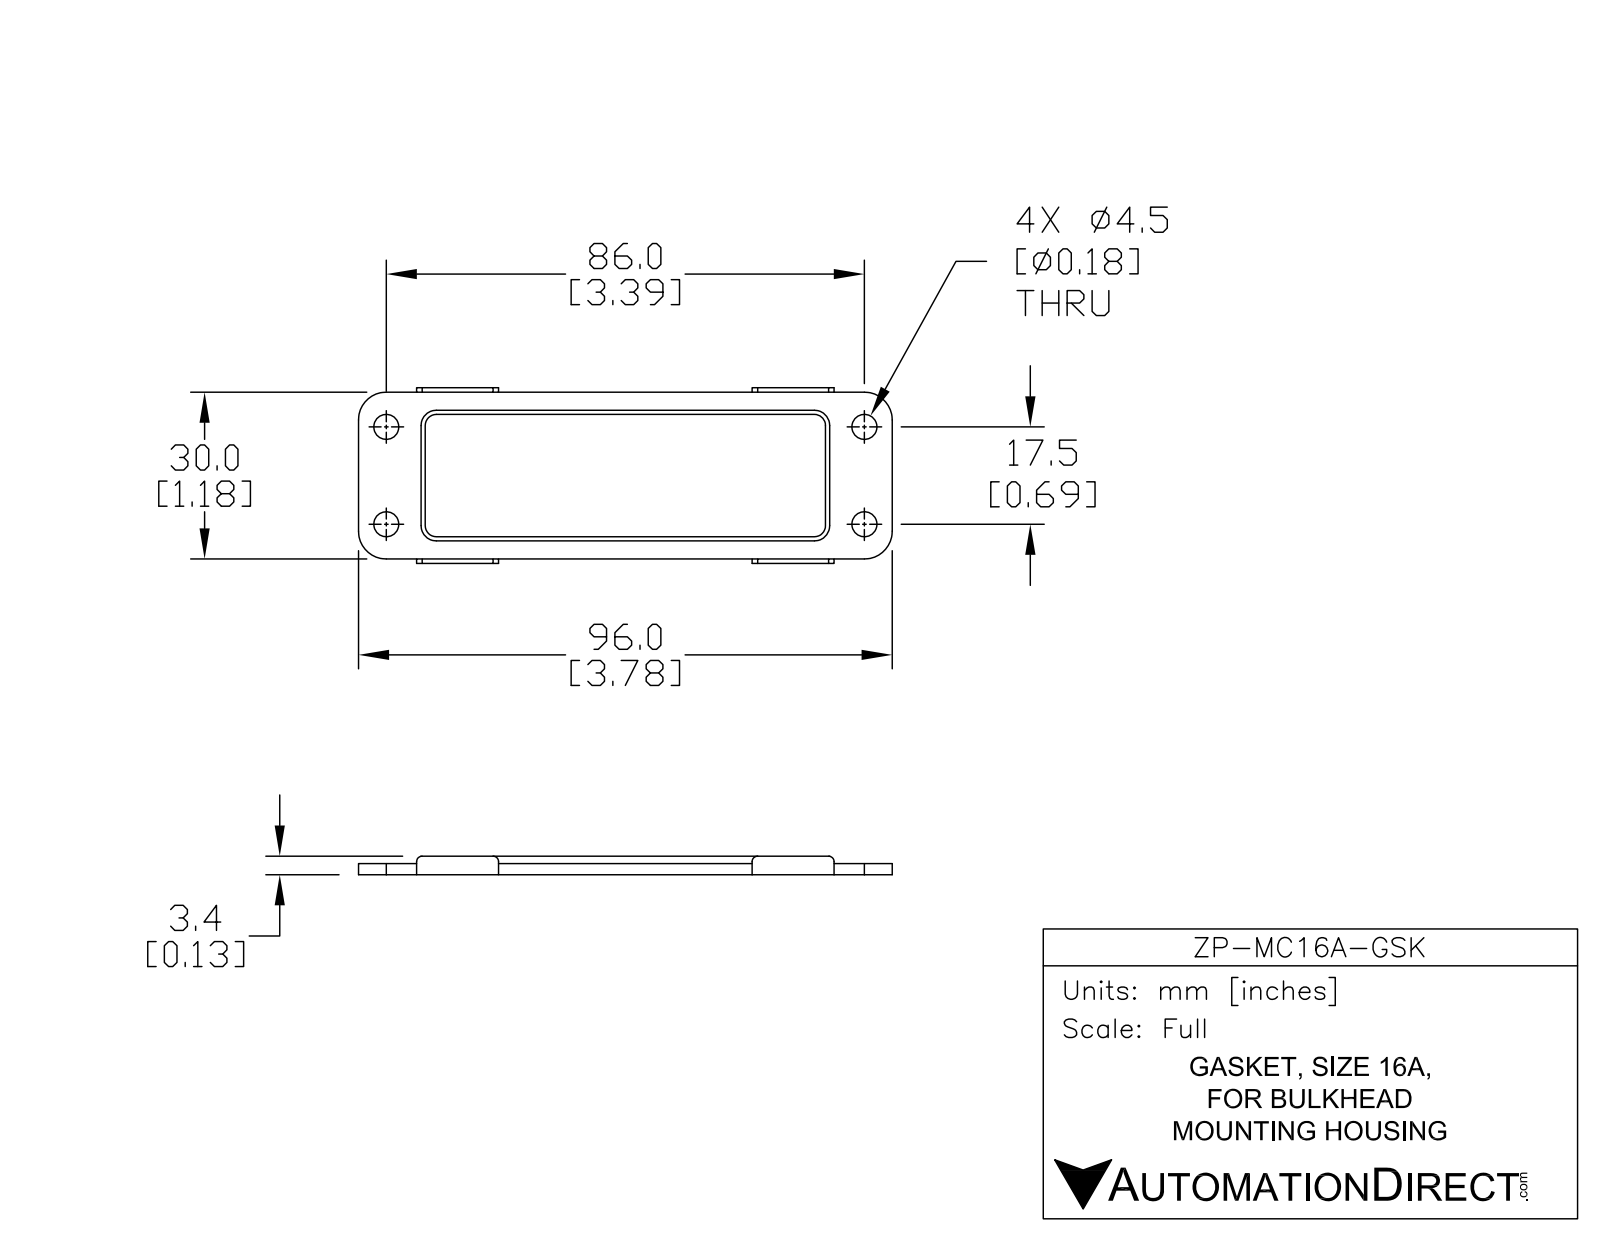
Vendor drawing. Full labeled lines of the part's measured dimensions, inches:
Part name (STEP PRODUCT): ZP-MC16A-GSK
STEP written by: SolidWorks 2014 (AUTOMOTIVE_DESIGN)
Units: inches
Bodies: 1 solid, 67 faces (39 planar, 28 cylindrical, 0 other)
Overall size (bounding box): 3.78 × 1.244 × 0.132
Volume: 0.169 in³ · Surface area: 6.465 in²
Round holes (diameter × count): ⌀0.177 ×4
Partial cylindrical surfaces — rounded edges, fillets, slot ends (radius × count): R0.039 ×4, R0.079 ×4, R0.108 ×4, R0.197 ×4
Main face-to-face distances: 0.079, 0.157, 1.024, 0.03, 0.866, 0.031, 0.189, 1.055, 1.213, 0.159
Hole centre spacings: 0.689, 3.386, 3.455
